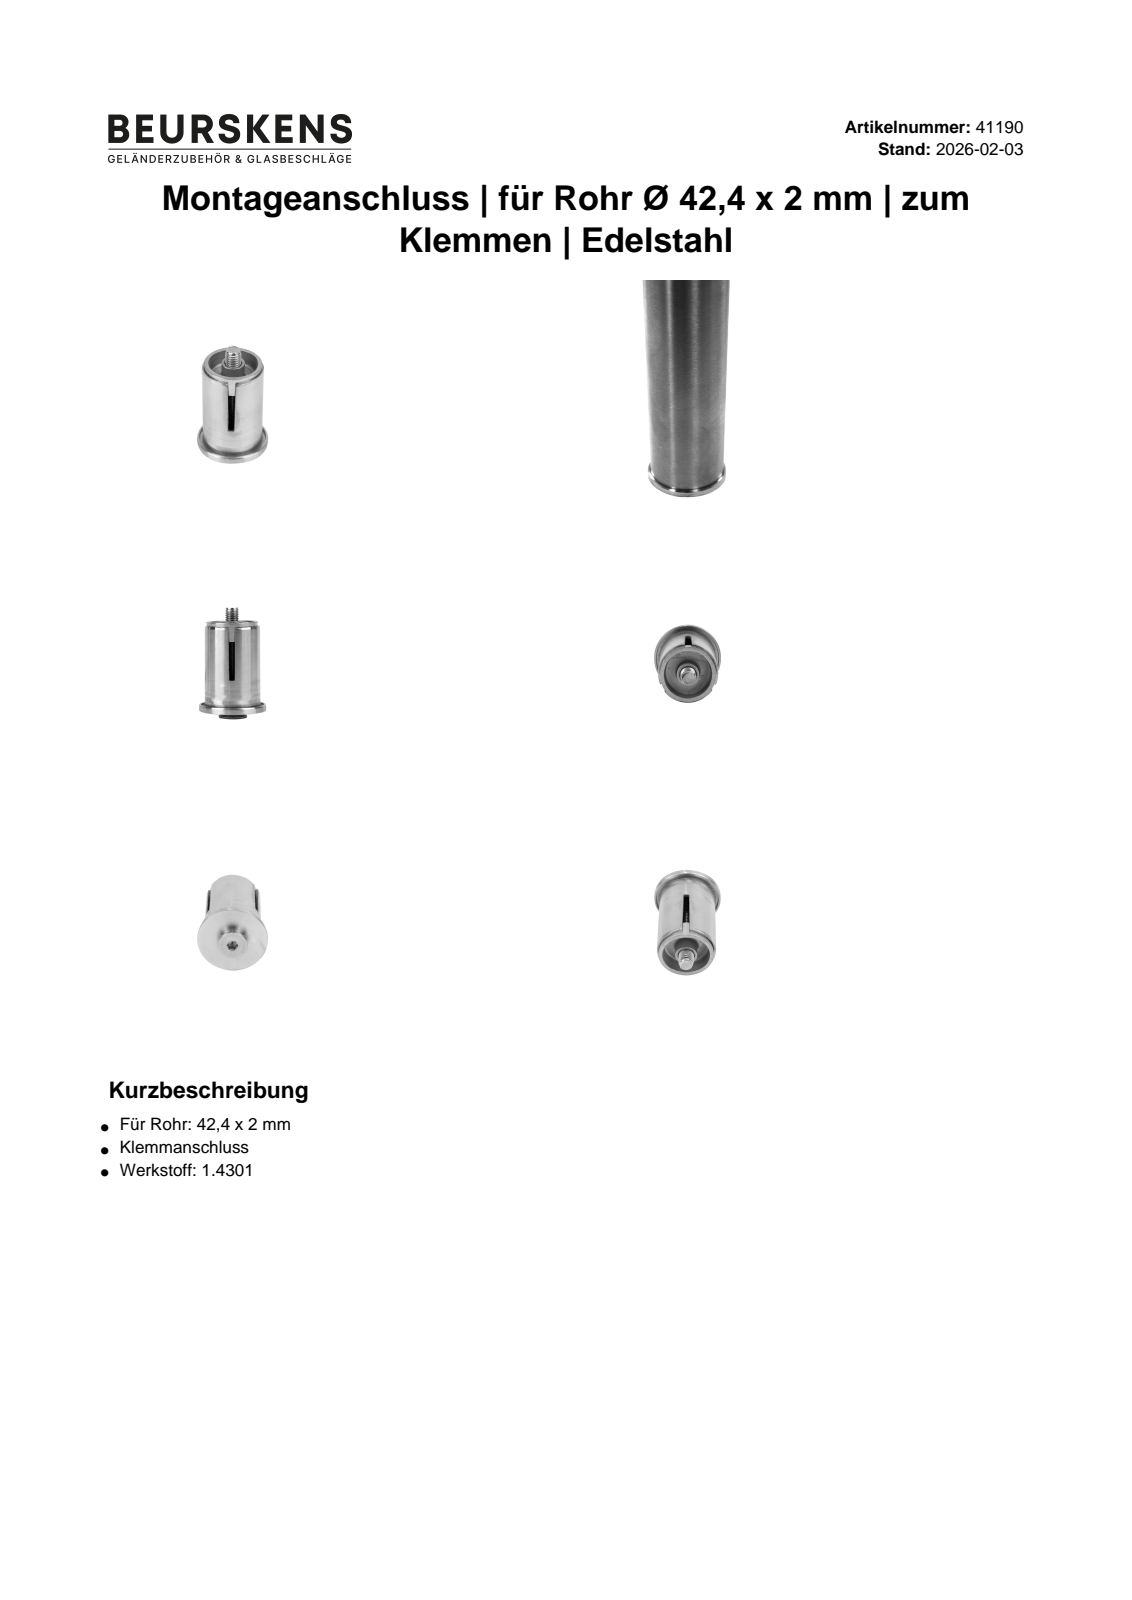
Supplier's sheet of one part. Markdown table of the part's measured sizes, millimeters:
| quantity | value |
| --- | --- |
| part name | 41190-2; socket countersunk head screw_iso_ISO 10642 - M10 x 80 --- 80N; 41190-1; 41190 for customer |
| STEP written by | SolidWorks 2020 (CONFIG_CONTROL_DESIGN) |
| units | millimeters |
| bodies | 3 solids, 68 faces (22 planar, 18 cylindrical, 28 other) |
| overall size | 80 × 46 × 46 |
| volume | 39 471 mm³ |
| surface area | 22 174 mm² |
| round holes (diameter × count) | 8.5 × 1, 11 × 1, 33 × 1, 42.7 × 1 |
| round bosses / shafts (diameter × count) | 46 × 1, 38.4 × 1, 38 × 1, 19.22 × 1, 10 × 1 |
| main face-to-face distances | 59.86, 13, 46.86, 2, 6, 53.86, 40.86, 4, 57.86, 44.86 |
